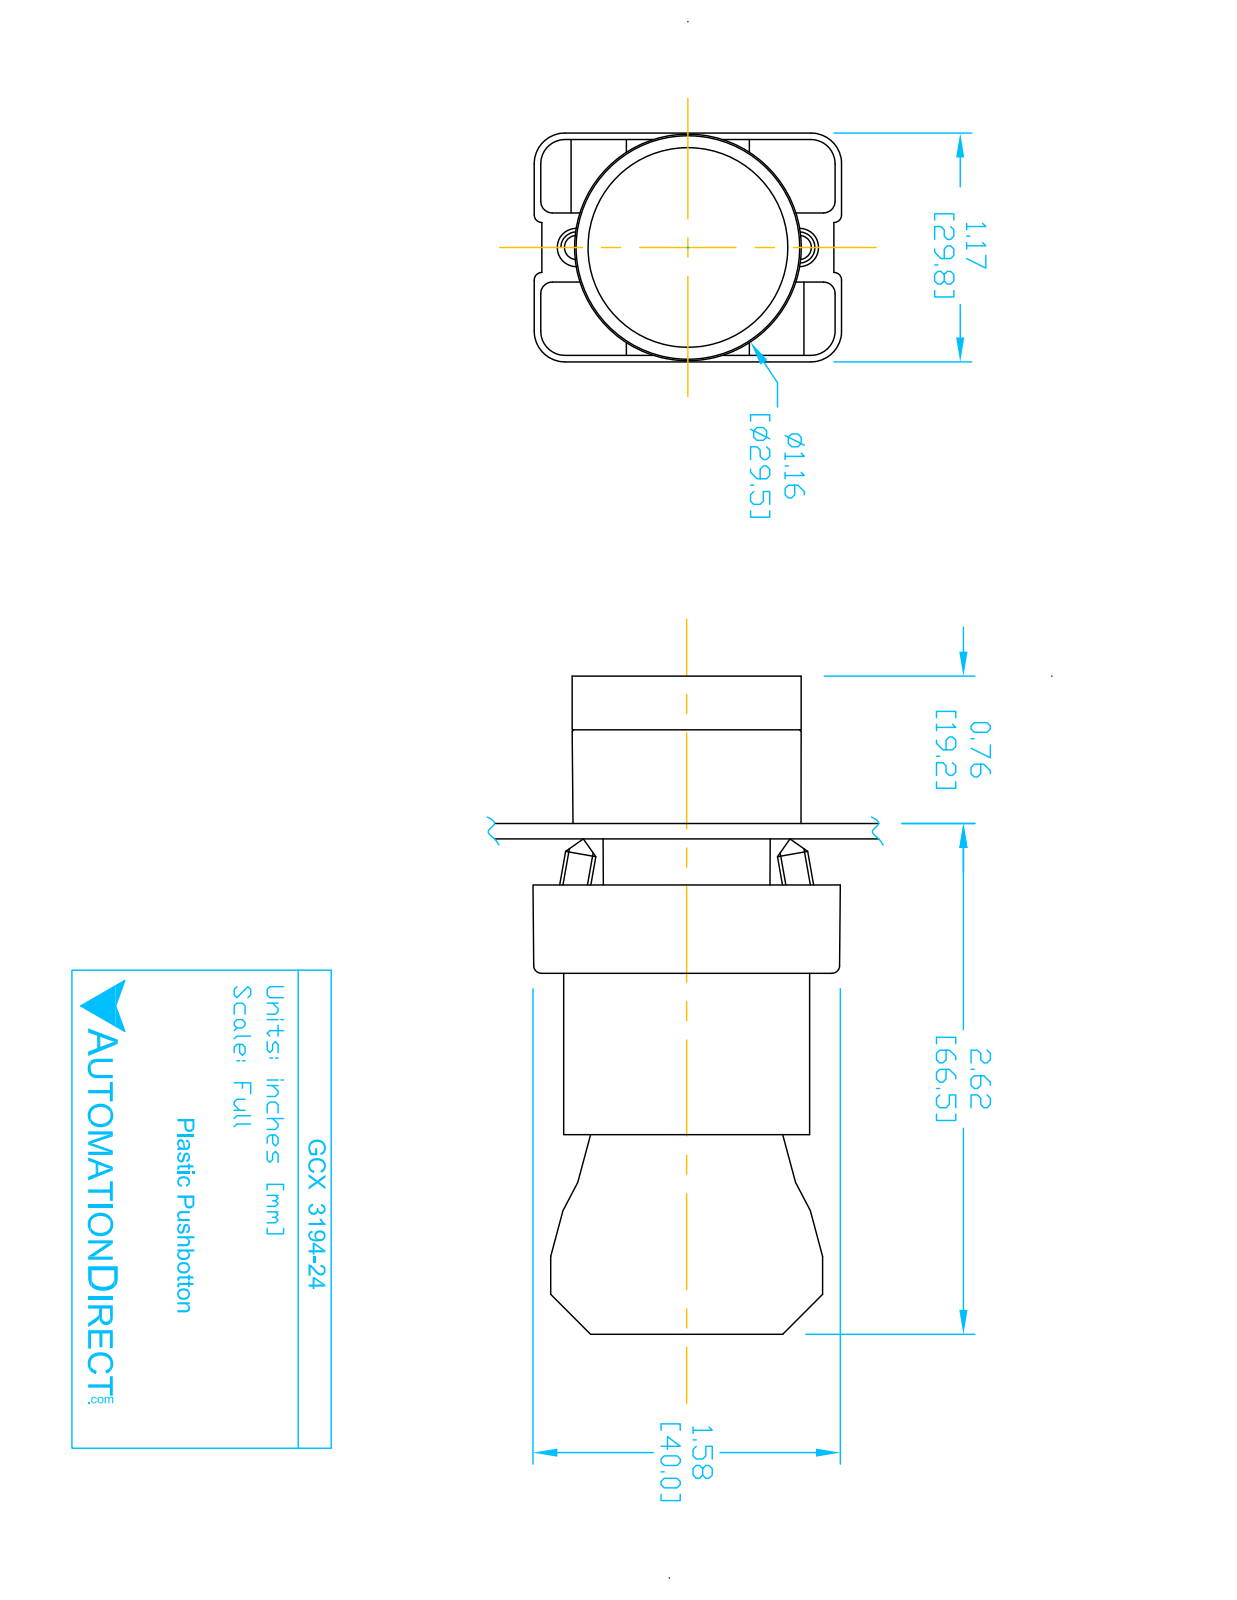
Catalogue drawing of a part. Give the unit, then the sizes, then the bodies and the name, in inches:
Units: inches
Overall size (bounding box): 3.319 × 1.581 × 1.177
Round holes (diameter × count): ⌀0.079 ×2, ⌀0.124 ×2, ⌀0.13 ×2, ⌀0.087 ×1, ⌀0.197 ×1, ⌀0.469 ×1, ⌀0.878 ×1, ⌀0.888 ×1, ⌀1.024 ×1
Round bosses / shafts (diameter × count): ⌀0.157 ×4, ⌀1.175 ×1, ⌀1.004 ×1, ⌀0.945 ×1, ⌀0.856 ×1, ⌀0.78 ×1, ⌀0.504 ×1
Partial cylindrical surfaces — rounded edges, fillets, slot ends (radius × count): R0.059 ×24, R0.041 ×12, R0.124 ×12, R0.157 ×12, R0.039 ×8, R0.128 ×2, R0.02 ×1, R0.063 ×1
Main face-to-face distances: 0.827, 0.579, 2.02, 1.193, 1.171, 0.276, 2.295, 1.469, 0.031, 0.033
Hole centre spacings: 0.236, 0.544, 0.472, 0.49
Volume: 2.794 in³ · Surface area: 38.77 in²
Bodies: 8 solids, 431 faces (252 planar, 148 cylindrical, 31 other)
Part name (STEP PRODUCT): CONTACT BLOCK; GCX3194-24; ECX1050; GCX3194 OPERATOR (+1 more)
STEP written by: SolidWorks 2016 (AUTOMOTIVE_DESIGN)
